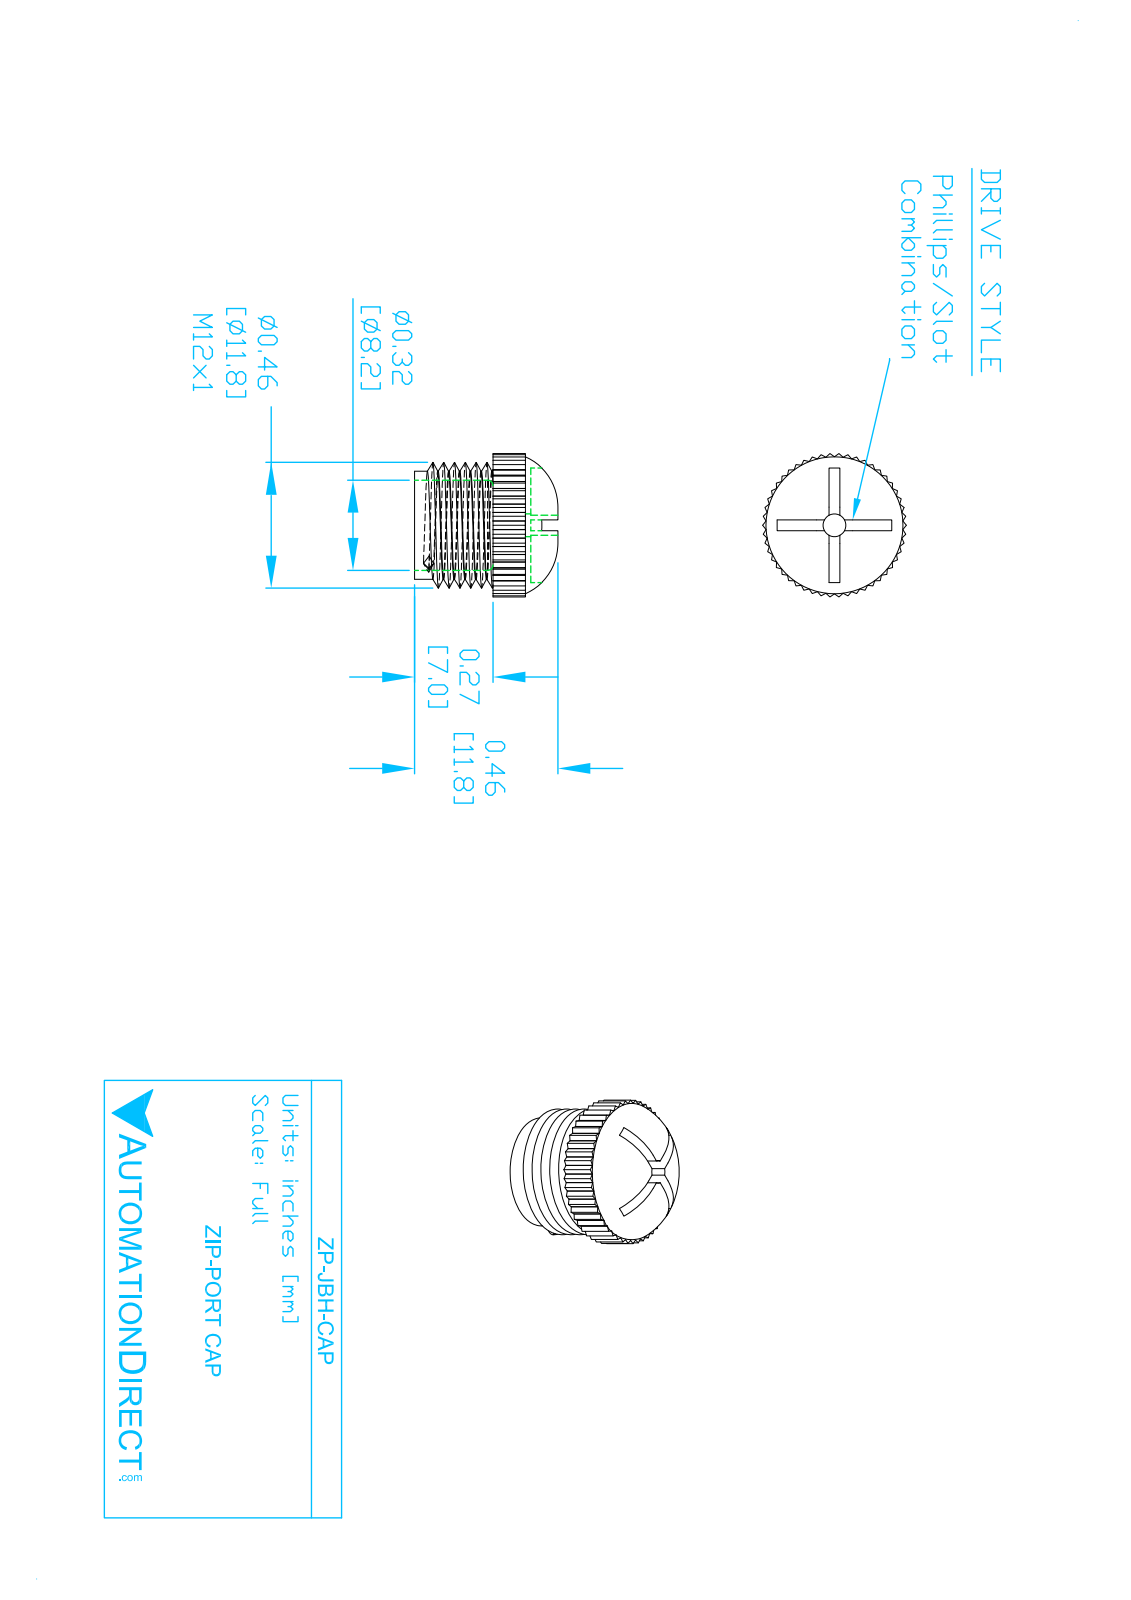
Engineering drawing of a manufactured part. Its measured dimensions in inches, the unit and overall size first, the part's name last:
Units: inches
Overall size (bounding box): 0.519 × 0.519 × 0.421
Round holes (diameter × count): ⌀0.118 ×1, ⌀0.33 ×1
Round bosses / shafts (diameter × count): ⌀0.489 ×1
Partial cylindrical surfaces — rounded edges, fillets, slot ends (radius × count): R0.26 ×1
Main face-to-face distances: 0.345, 0.305, 0.077, 0.382, 0.345, 0.152, 0.075, 0.23, 0.043, 0.053
Volume: 0.043 in³ · Surface area: 1.71 in²
Bodies: 1 solid, 242 faces (132 planar, 53 cylindrical, 57 other)
Part name (STEP PRODUCT): MDC-PLUG-PA
STEP written by: SolidWorks 2007 (AUTOMOTIVE_DESIGN)
